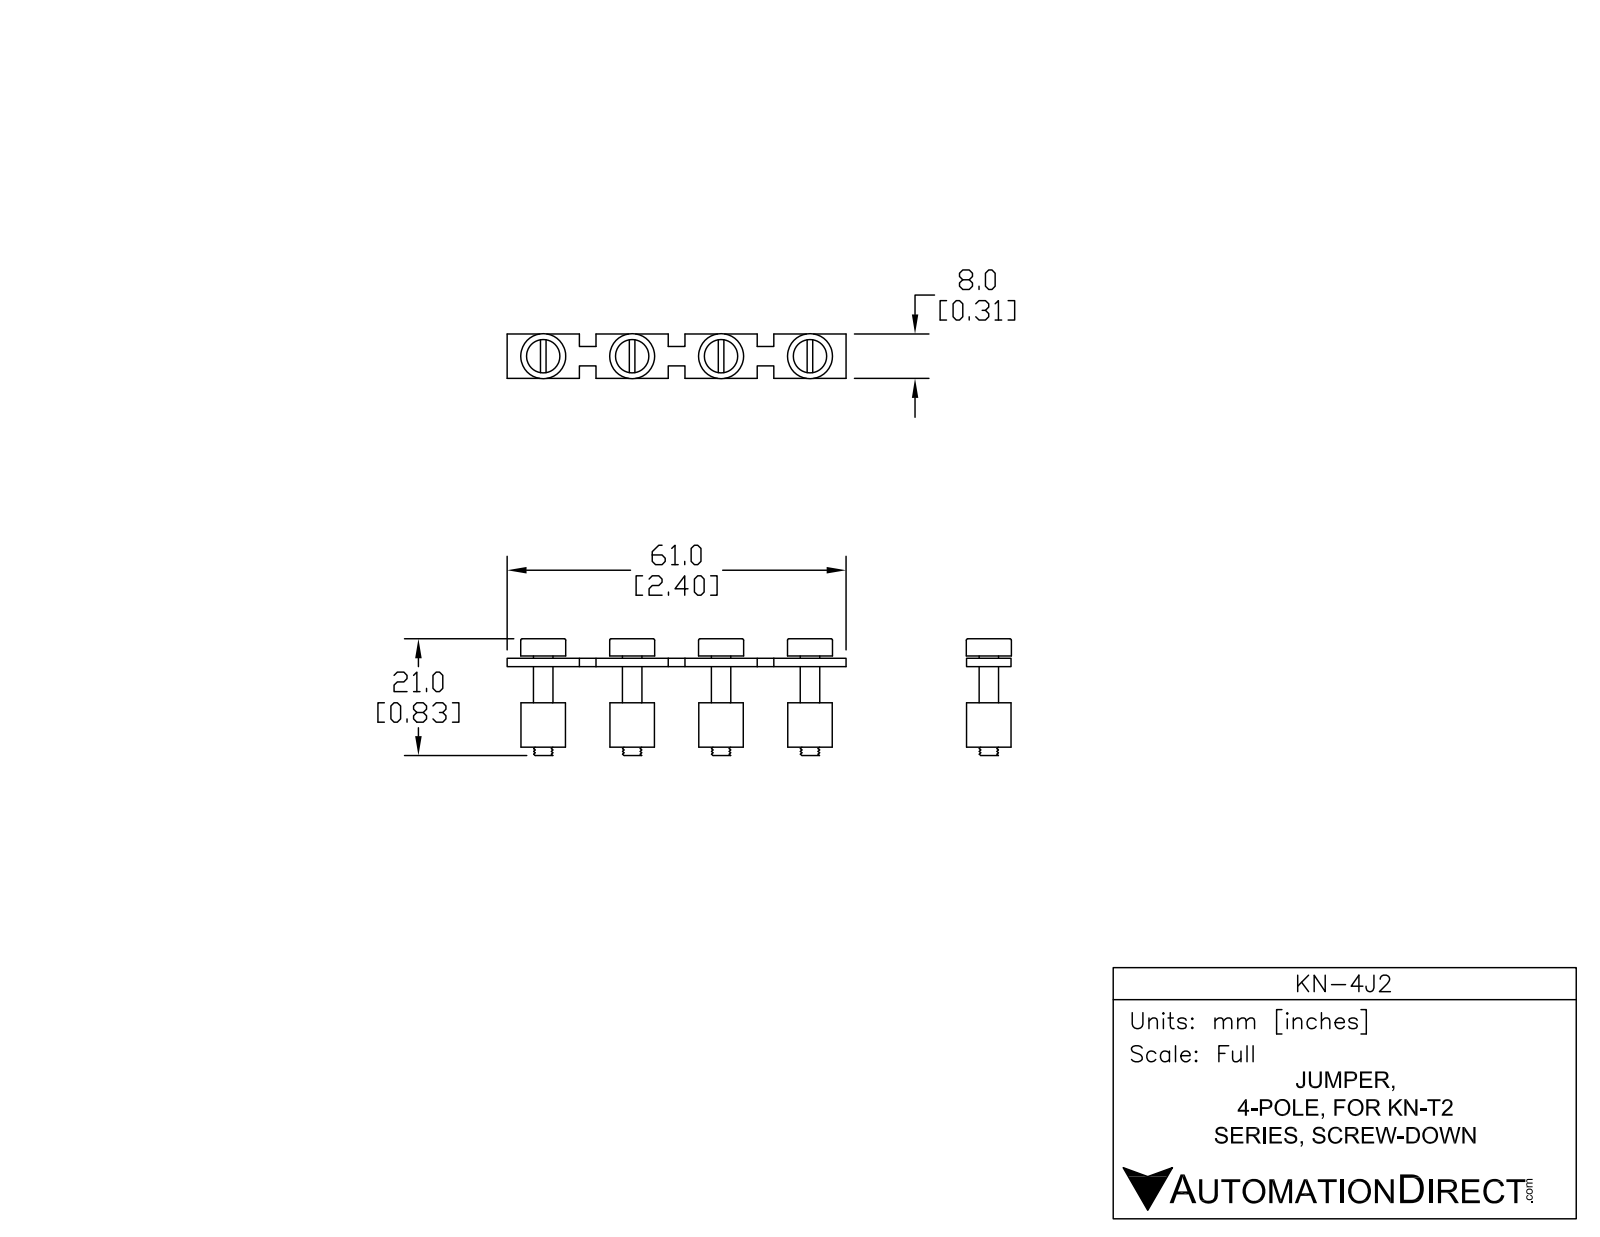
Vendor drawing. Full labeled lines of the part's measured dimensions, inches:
Part name (STEP PRODUCT): KN-4J2
STEP written by: SolidWorks 2014 (AUTOMOTIVE_DESIGN)
Units: inches
Bodies: 13 solids, 166 faces (82 planar, 60 cylindrical, 24 other)
Overall size (bounding box): 2.402 × 0.827 × 0.319
Volume: 0.178 in³ · Surface area: 7.476 in²
Round holes (diameter × count): ⌀0.177 ×4, ⌀0.236 ×4
Round bosses / shafts (diameter × count): ⌀0.319 ×4, ⌀0.315 ×4, ⌀0.266 ×4, ⌀0.138 ×4
Main face-to-face distances: 0.059, 0.177, 0.315, 0.118, 0.236, 0.02, 0.354, 0.138, 0.63, 0.492
Hole centre spacings: 0.63, 1.26, 1.89
